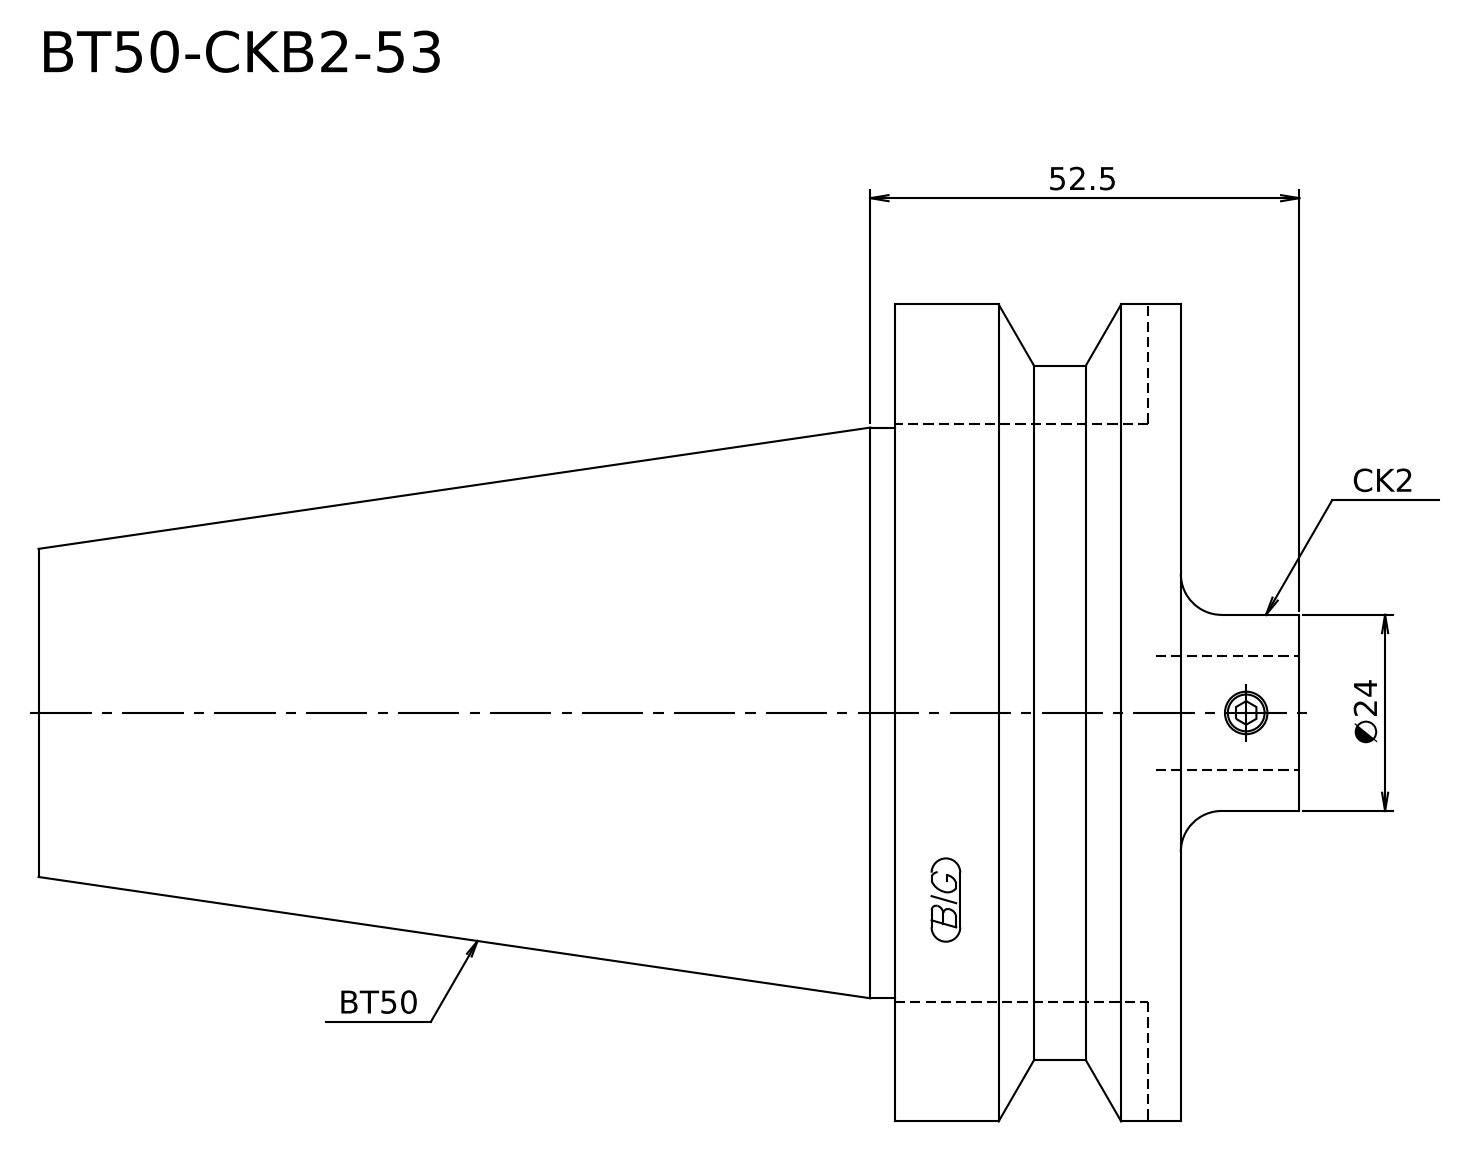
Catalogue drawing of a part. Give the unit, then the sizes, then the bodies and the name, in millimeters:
Units: millimetres
Overall size (bounding box): 154.3 × 100 × 100
Round bosses / shafts (diameter × count): ⌀100 ×1, ⌀85 ×1, ⌀69.85 ×1, ⌀24 ×1
Main face-to-face distances: 35, 139.8, 104.8, 14.5, 49.5, 154.3
Volume: 518 278 mm³ · Surface area: 45 492 mm²
Bodies: 1 solid, 13 faces (4 planar, 5 cylindrical, 4 other)
STEP written by: Kubotek KeyCreator V8.5.1 (14335) (CONFIG_CONTROL_DESIGN)
